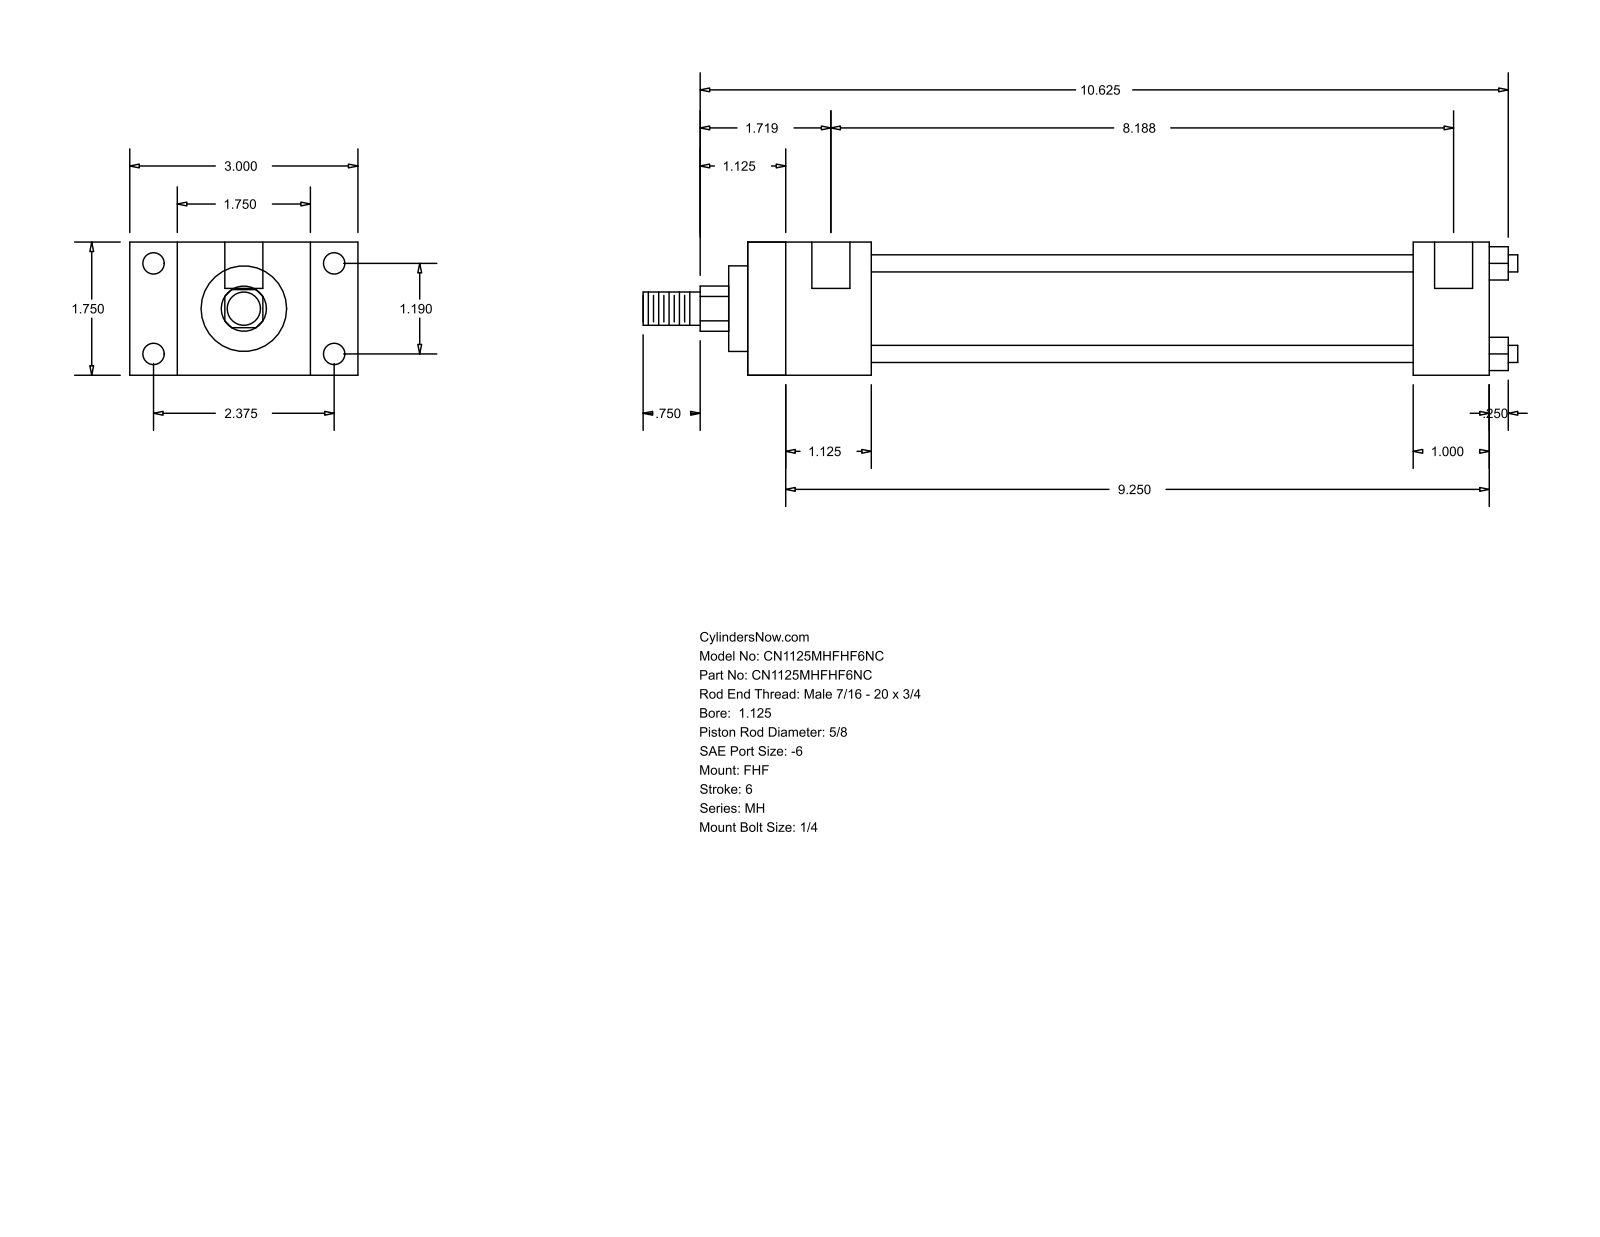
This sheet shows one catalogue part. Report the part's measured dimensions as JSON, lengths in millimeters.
{"part_name": "MH_FHF__0112_0.625", "step_written_by": "GSSL Pune (CONFIG_CONTROL_DESIGN)", "units": "millimeters", "bodies": {"solids": 0, "faces": 88, "planar": 60, "cylindrical": 28, "other": 0}, "overall_size": [292.1, 76.2, 44.45], "round_holes": [[5.56, 4], [7.14, 4], [12.7, 2]], "round_bosses_or_shafts": [[5.71, 4], [34.92, 1], [28.57, 1], [15.88, 1], [11.11, 1]], "partial_cylinders_radius": [[7.54, 1]], "face_to_face_distances": [44.46, 15.87, 60.33, 41.27, 76.2, 247.64, 206.37, 25.4, 222.24, 180.97], "hole_center_spacings": [30.22, 60.32, 67.47, 204.79, 3.17, 207.96]}
